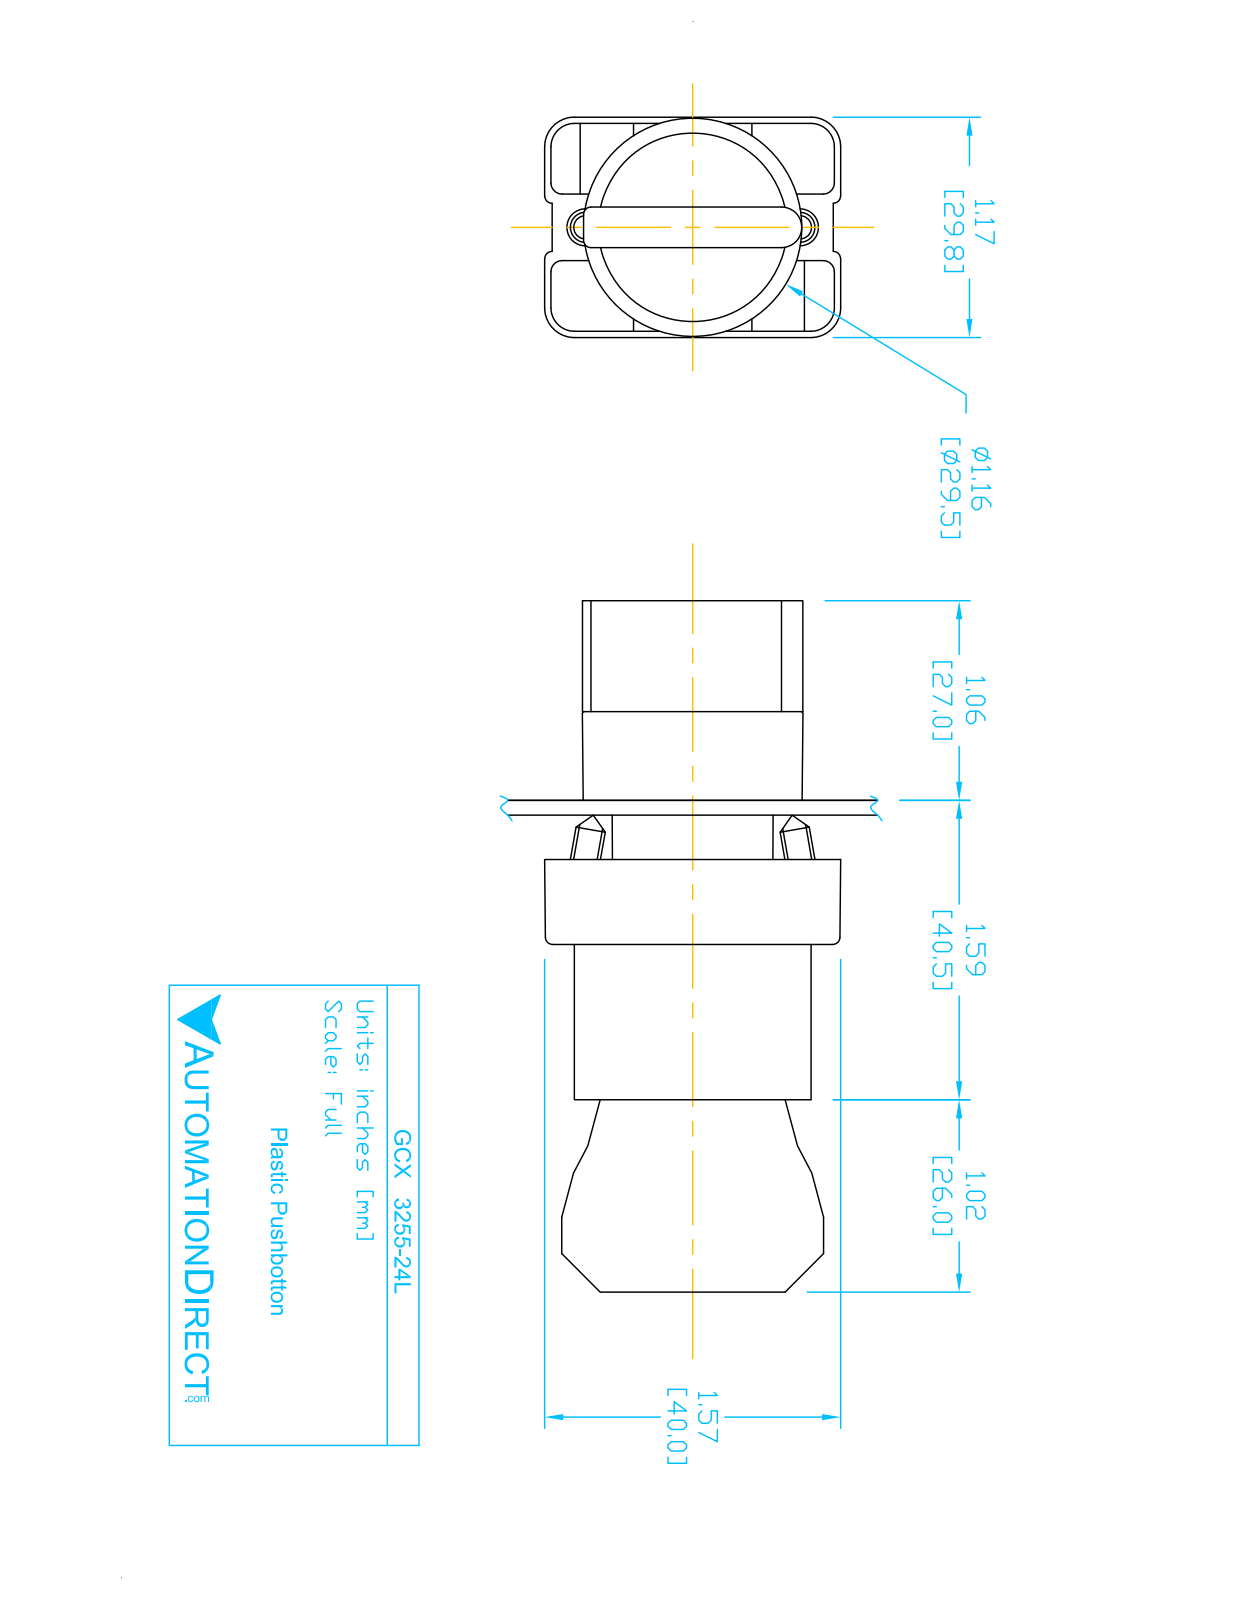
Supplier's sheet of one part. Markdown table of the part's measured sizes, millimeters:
| quantity | value |
| --- | --- |
| part name | ECX1050; GCX3255L OPERATOR; GCX3255-24L; ecx1040 (+1 more) |
| STEP written by | SolidWorks 2016 (AUTOMOTIVE_DESIGN) |
| units | millimeters |
| bodies | 8 solids, 445 faces (263 planar, 151 cylindrical, 31 other) |
| overall size | 92.8 × 40.2 × 29.9 |
| volume | 45 870 mm³ |
| surface area | 25 160 mm² |
| round holes (diameter × count) | 2 × 2, 3.1 × 2, 3.3 × 2, 2.2 × 1, 5 × 1, 11.9 × 1, 22.3 × 1, 22.6 × 1, 26 × 1 |
| round bosses / shafts (diameter × count) | 4 × 4, 29.8 × 1, 25.5 × 1, 24 × 1, 21.7 × 1, 19.8 × 1, 12.8 × 1 |
| partial cylindrical surfaces (radius × count) | 1.5 × 24, 1 × 12, 3.1 × 12, 4 × 12, 1 × 9, 3.3 × 2, 0.5 × 1, 1.6 × 1 |
| main face-to-face distances | 21, 51.3, 30.3, 14.7, 31.6, 29.7, 12, 11.9, 0.8, 0.8 |
| hole center spacings | 6, 13.8, 12, 12.4 |
